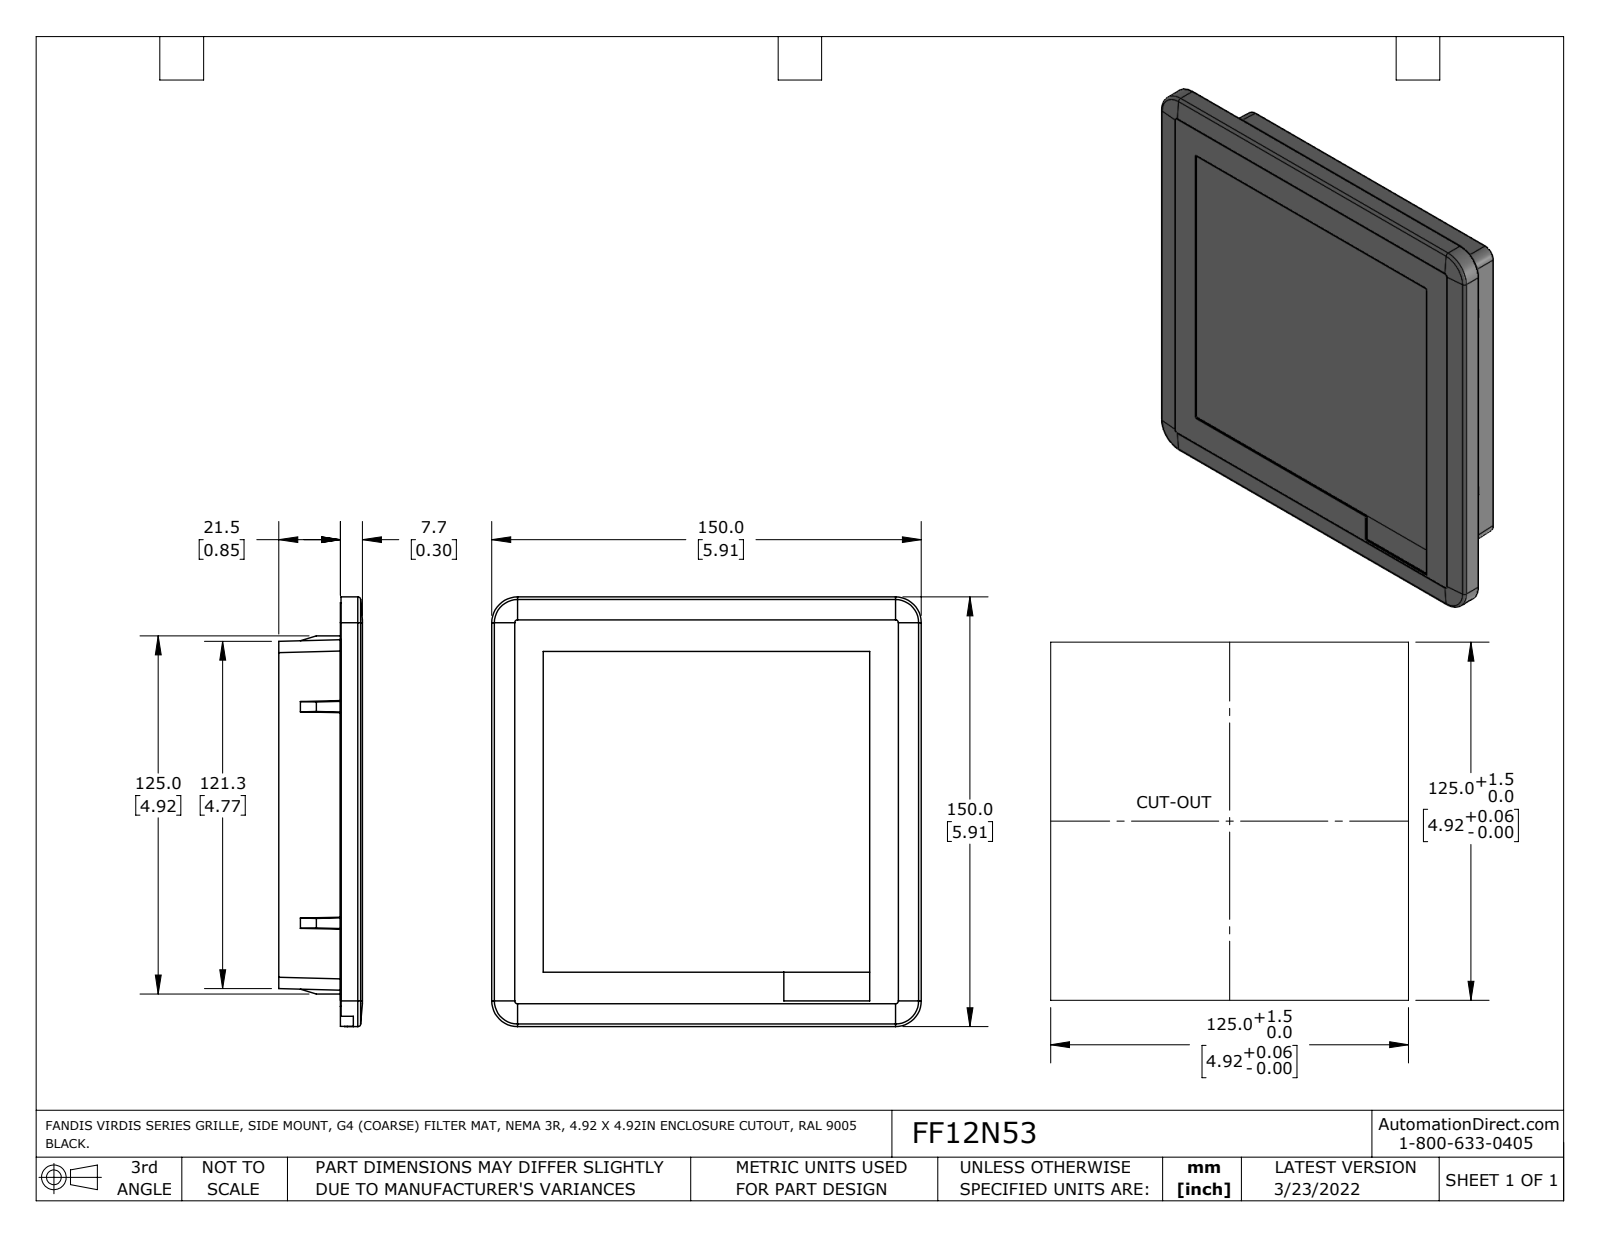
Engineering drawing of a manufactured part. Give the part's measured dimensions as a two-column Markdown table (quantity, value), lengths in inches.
| quantity | value |
| --- | --- |
| part name | FF12y-125 type 3R (p.c.) |
| STEP written by | SolidWorks 2021 (AUTOMOTIVE_DESIGN) |
| units | inches |
| bodies | 1 solid, 194 faces (129 planar, 35 cylindrical, 30 other) |
| overall size | 5.906 × 5.906 × 1.15 |
| volume | 29.33 in³ |
| surface area | 99.82 in² |
| partial cylindrical surfaces (radius × count) | 0.008 × 7, 0.039 × 4, 0.098 × 4, 0.157 × 4, 0.276 × 4, 0.354 × 4, 0.283 × 2, 1.28 × 1 |
| main face-to-face distances | 1.13, 0.283, 0.846, 0.02, 0.303, 1.15, 0.071, 5.823, 5.835, 0.083 |
